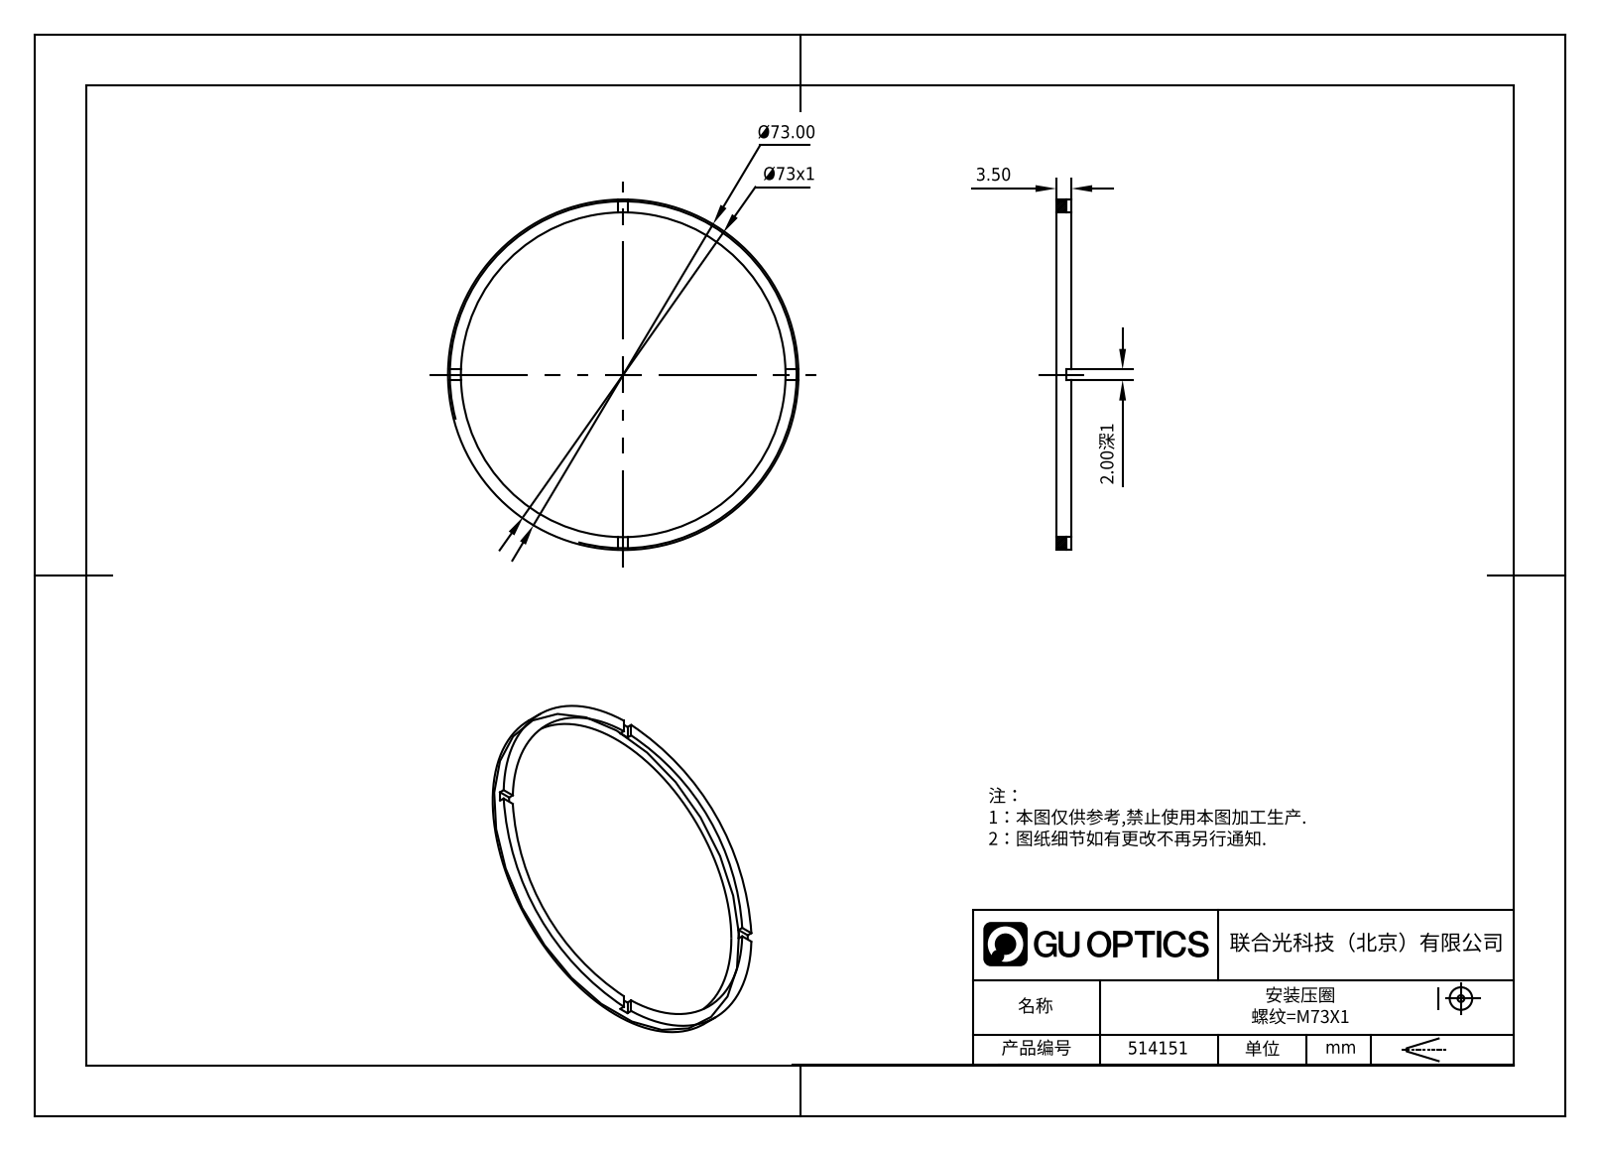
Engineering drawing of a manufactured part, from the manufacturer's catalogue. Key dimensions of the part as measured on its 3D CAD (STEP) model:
Part name (STEP PRODUCT): 514151
STEP written by: SolidWorks 2020 (CONFIG_CONTROL_DESIGN)
Units: millimetres
Bodies: 1 solid, 21 faces (17 planar, 4 cylindrical, 0 other)
Overall size (bounding box): 73 × 73 × 3.5
Volume: 2 285 mm³ · Surface area: 2 867 mm²
Round holes (diameter × count): ⌀67 ×1
Round bosses / shafts (diameter × count): ⌀73 ×1
Main face-to-face distances: 3.5, 2.5, 1, 2
